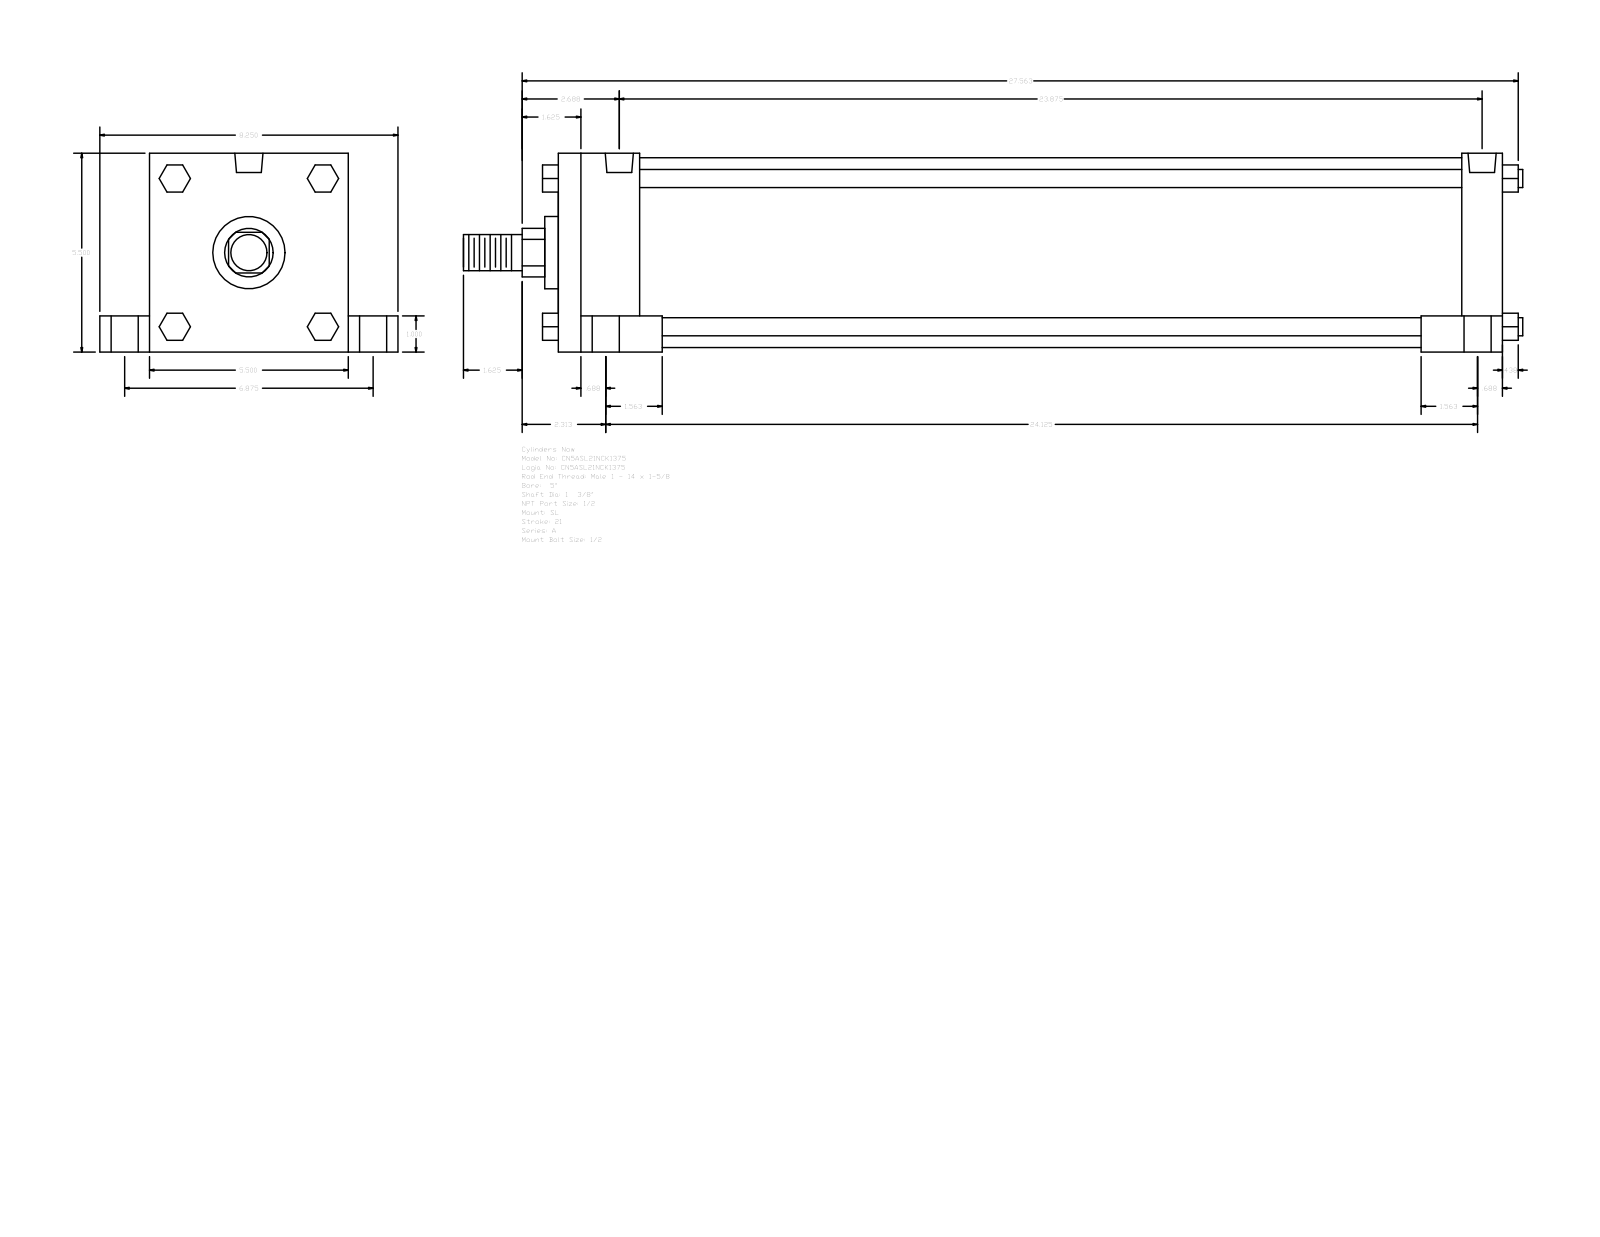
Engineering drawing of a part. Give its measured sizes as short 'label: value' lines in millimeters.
name: A_SL__0500_1.375
written by: GSSL Pune (CONFIG_CONTROL_DESIGN)
unit: mm
bodies: 0 solids, 150 faces (114 planar, 36 cylindrical, 0 other)
size: 744.54 × 209.55 × 139.7
holes: 4× ⌀8.73, 4× ⌀19.05, 4× ⌀25.4, 2× ⌀19.77
bosses: 4× ⌀12.7, 1× ⌀133.35, 1× ⌀50.8, 1× ⌀34.92, 1× ⌀25.4
rounds: 1× R17.06
face distances: 139.7, 663.58, 57.15, 606.43, 25.4, 114.3, 34.93, 174.63, 28.58, 635
hole spacings: 2.39, 87.31, 87.37, 87.83, 88.12, 174.62, 601.65, 604.04
